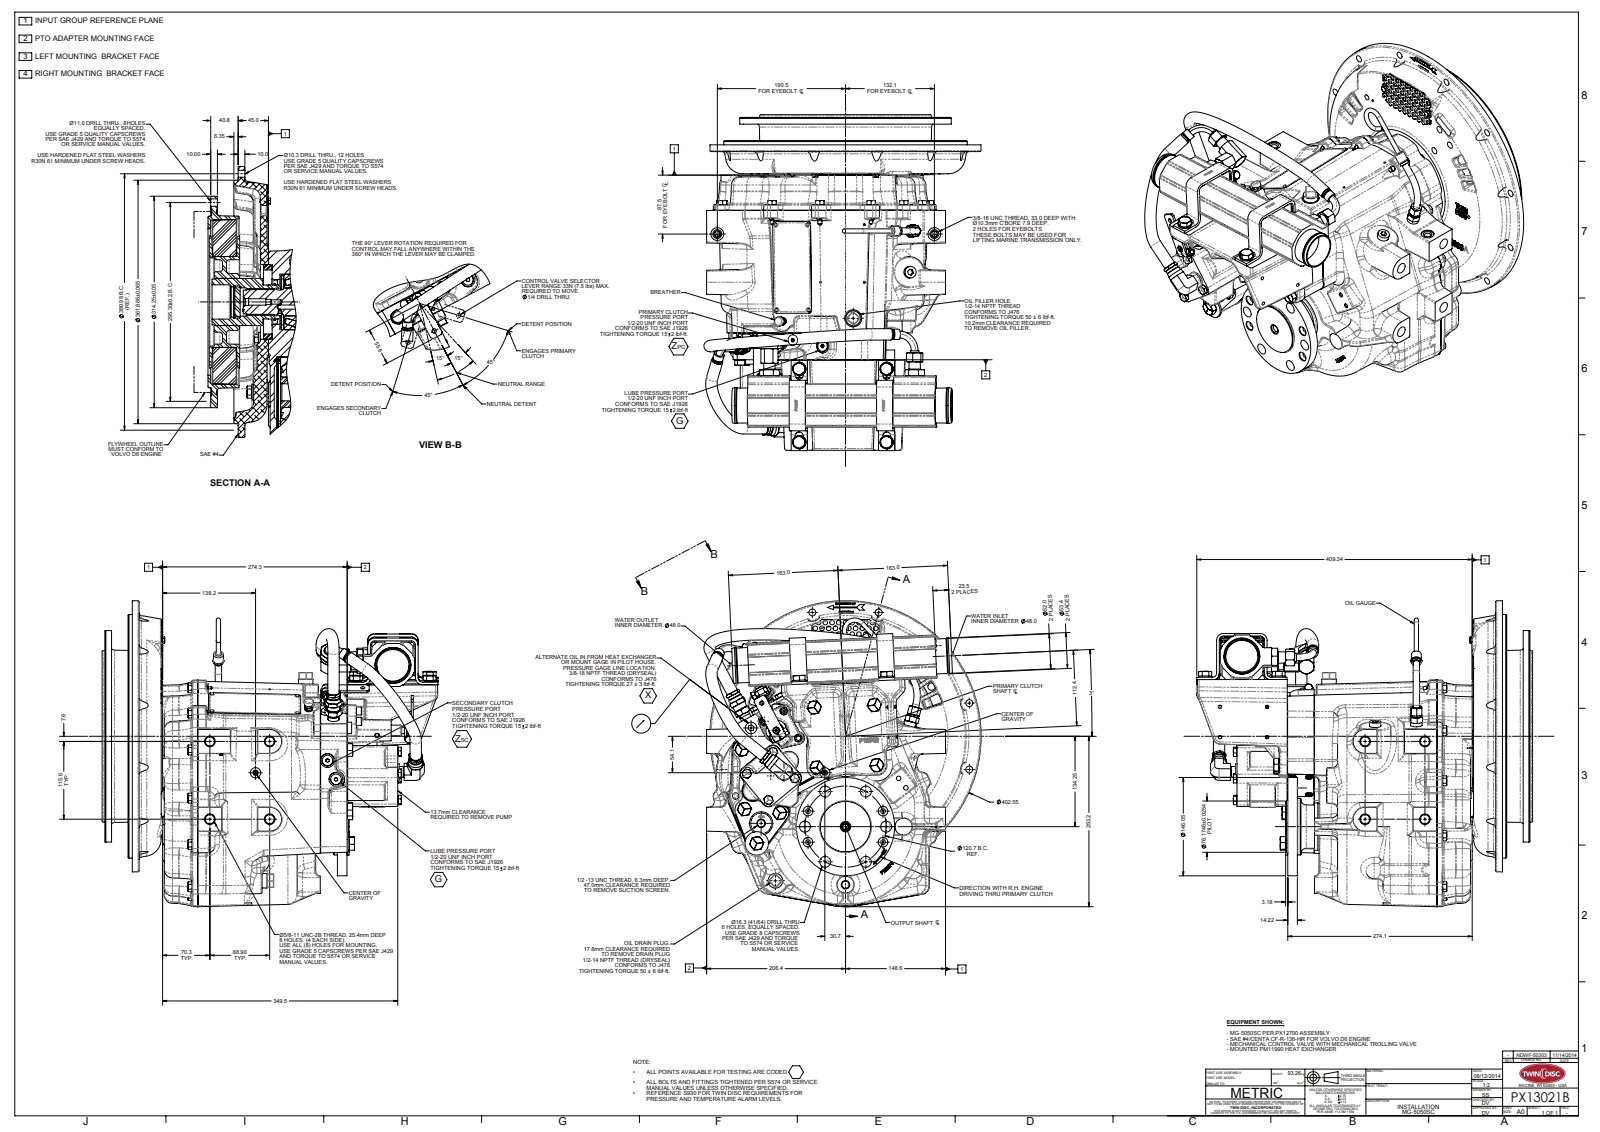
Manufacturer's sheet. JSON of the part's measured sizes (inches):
{"part_name": "PX13021B", "step_written_by": "SolidWorks 2010 (AUTOMOTIVE_DESIGN)", "units": "inches", "bodies": {"solids": 0, "faces": 4287, "planar": 1079, "cylindrical": 1188, "other": 2020}, "overall_size": [19.651, 17.903, 16.217], "round_holes": [[0.276, 51], [0.406, 14], [0.433, 8], [0.375, 7], [0.641, 6], [0.313, 5], [0.111, 4], [0.197, 4], [0.281, 4], [0.563, 4], [0.406, 3], [0.625, 3]], "round_bosses_or_shafts": [[0.494, 6], [0.743, 5], [0.781, 4], [0.665, 4], [0.625, 4], [0.25, 4], [0.599, 3], [0.469, 3]], "partial_cylinders_radius": [[0.059, 90], [0.06, 64], [0.32, 62], [0.315, 49], [0.016, 31], [0.118, 27], [0.4, 23], [0.512, 20]], "face_to_face_distances": [0.394, 1.299, 1.606, 9.303, 0.079, 1.378, 0.026, 9.329, 9.15, 9.124], "hole_center_spacings": [0.394, 7.5, 10.606, 12.99, 0.787, 1.181, 2.756, 3.882]}
